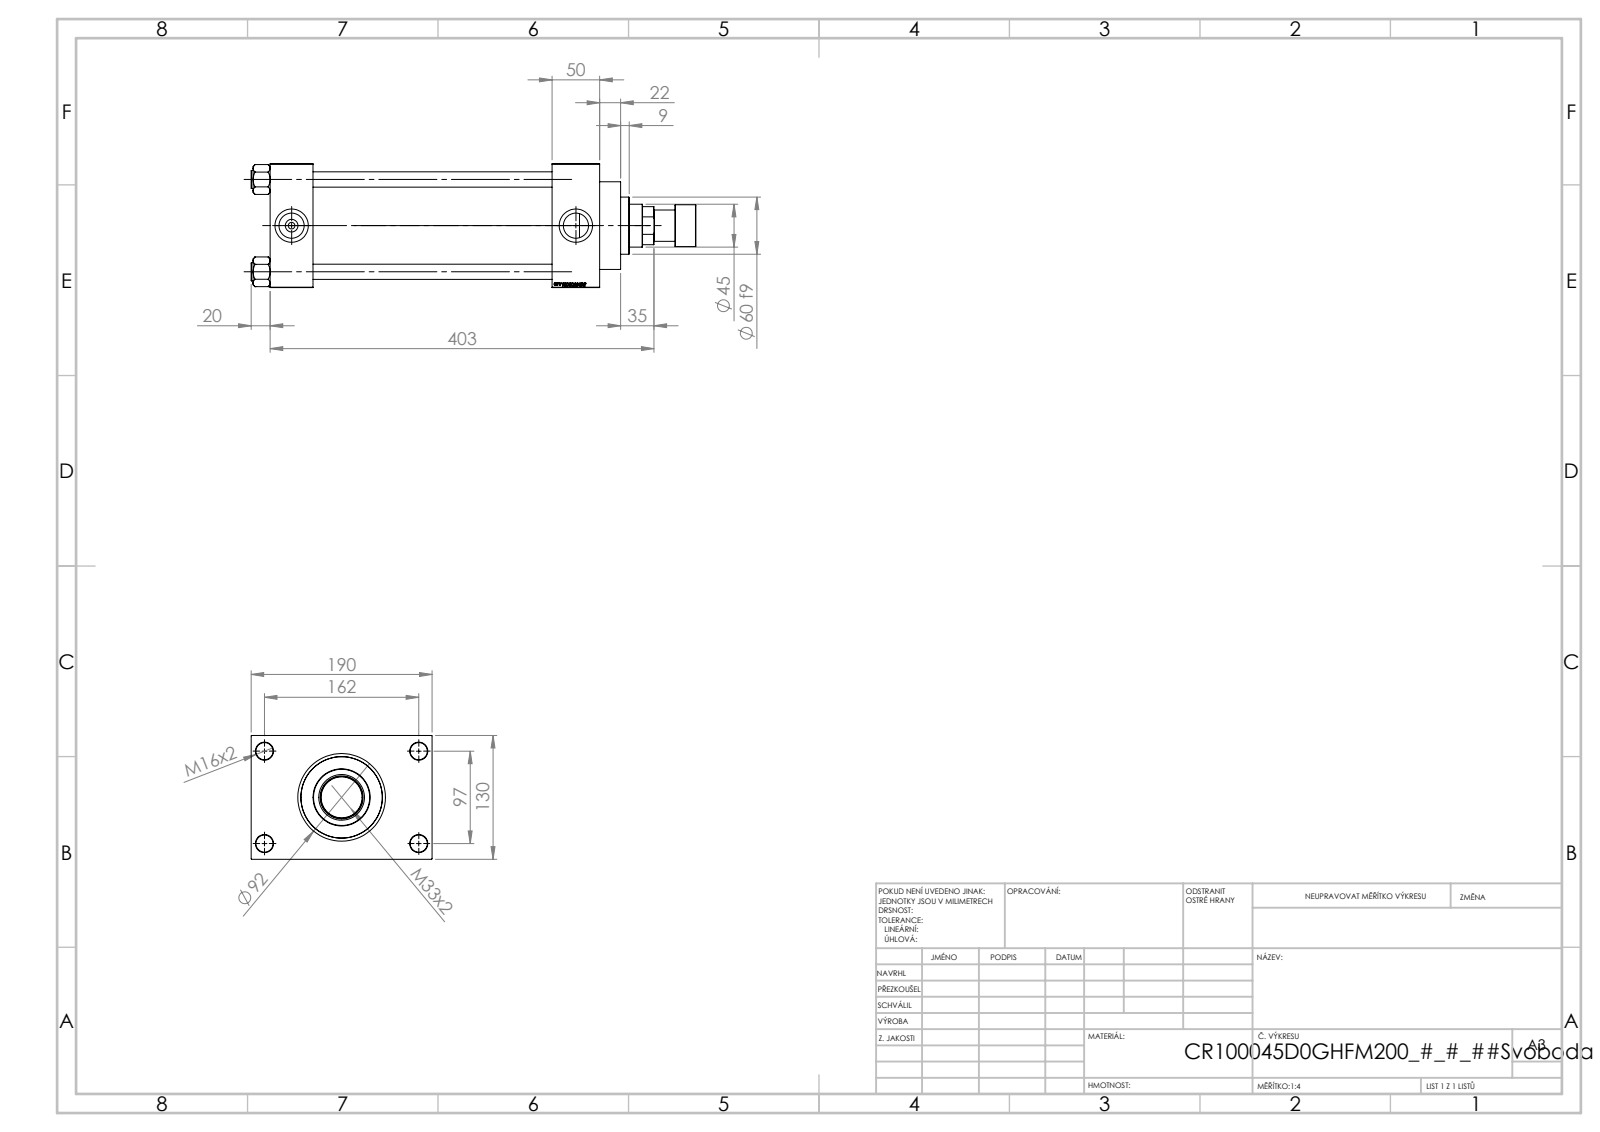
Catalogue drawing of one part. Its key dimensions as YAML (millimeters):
part_name: "NUT_M5_D; V215_VC_A; V215CR_ROD_END_F; V215CR_D_TYCINKA (+2 more)"
step_written_by: "SolidWorks 2019 (CONFIG_CONTROL_DESIGN)"
units: millimeters
bodies: {solids: 12, faces: 1164, planar: 548, cylindrical: 92, other: 524}
overall_size: [467, 190, 130]
volume: 3249000
surface_area: 541384
round_holes:
  - {diameter: 16, count: 4}
  - {diameter: 18, count: 4}
  - {diameter: 7, count: 2}
  - {diameter: 26.44, count: 2}
  - {diameter: 35, count: 2}
  - {diameter: 31.5, count: 1}
  - {diameter: 45, count: 1}
  - {diameter: 48, count: 1}
  - {diameter: 76, count: 1}
  - {diameter: 85.5, count: 1}
  - {diameter: 100, count: 1}
round_bosses_or_shafts:
  - {diameter: 19, count: 4}
  - {diameter: 106, count: 1}
  - {diameter: 92, count: 1}
  - {diameter: 60, count: 1}
  - {diameter: 44, count: 1}
  - {diameter: 33, count: 1}
face_to_face_distances: [130, 45, 296, 251, 346, 301, 50, 30, 160, 96]
hole_center_spacings: [32.55, 68.52, 94.41, 96.9, 102.27, 129.45, 161.73, 97]
